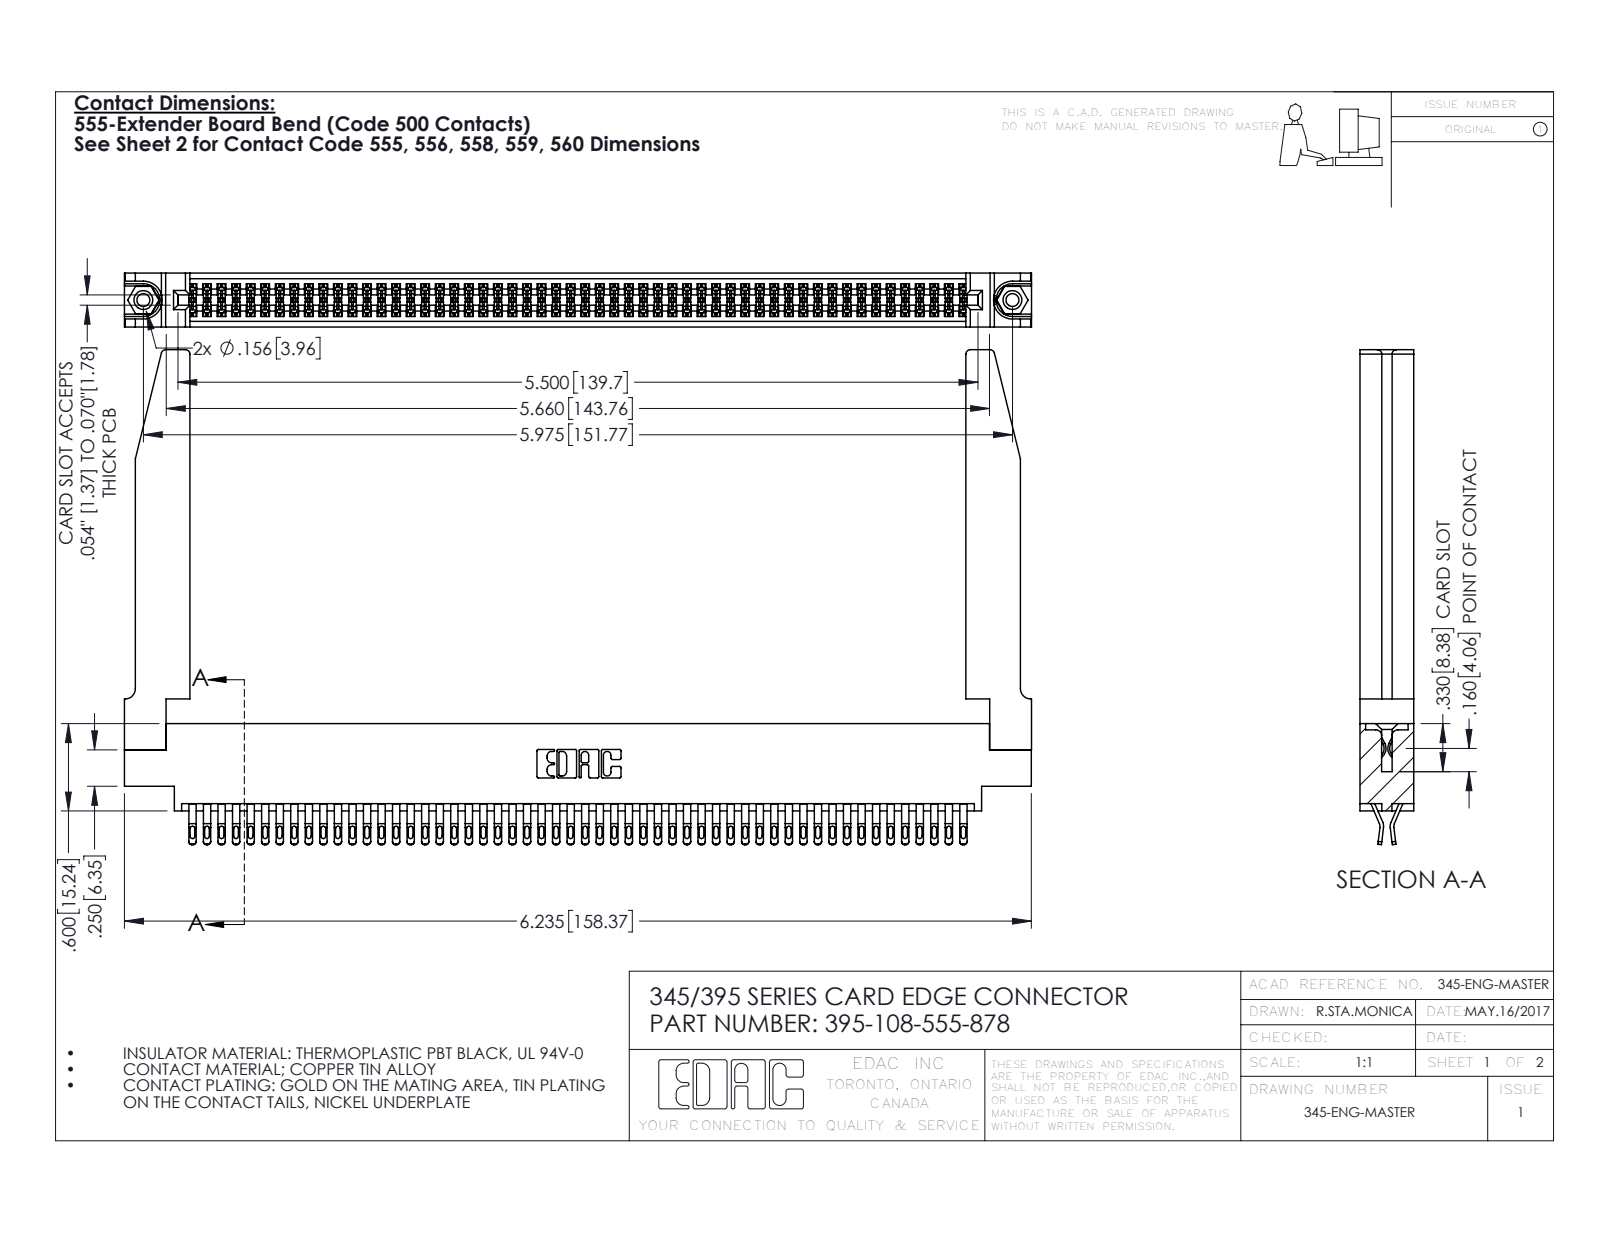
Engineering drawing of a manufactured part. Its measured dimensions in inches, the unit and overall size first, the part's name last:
Units: inches
Overall size (bounding box): 6.236 × 3.402 × 0.37
Round holes (diameter × count): ⌀0.089 ×2, ⌀0.125 ×2, ⌀0.156 ×2, ⌀0.064 ×1
Round bosses / shafts (diameter × count): ⌀0.155 ×2
Partial cylindrical surfaces — rounded edges, fillets, slot ends (radius × count): R0.016 ×270, R0.02 ×216, R0.006 ×162, R0.01 ×22, R0.03 ×8, R0.007 ×6, R0.031 ×6, R0.026 ×3
Main face-to-face distances: 0.37, 0.072, 0.298, 0.025, 0.098, 0.272, 0.2, 0.225, 0.175, 0.148
Hole centre spacings: 0.27, 5.739, 5.975
Volume: 1.432 in³ · Surface area: 48.84 in²
Bodies: 113 solids, 6412 faces (3574 planar, 2786 cylindrical, 52 other)
Part name (STEP PRODUCT): 345 Part_0.170 Offset - 0.156 Dia-TH; 395-108-555-878; 345-250-001_345-250-001-102; 345-220-078_345-220-078 (+1 more)
STEP written by: SolidWorks 2016 (CONFIG_CONTROL_DESIGN)
